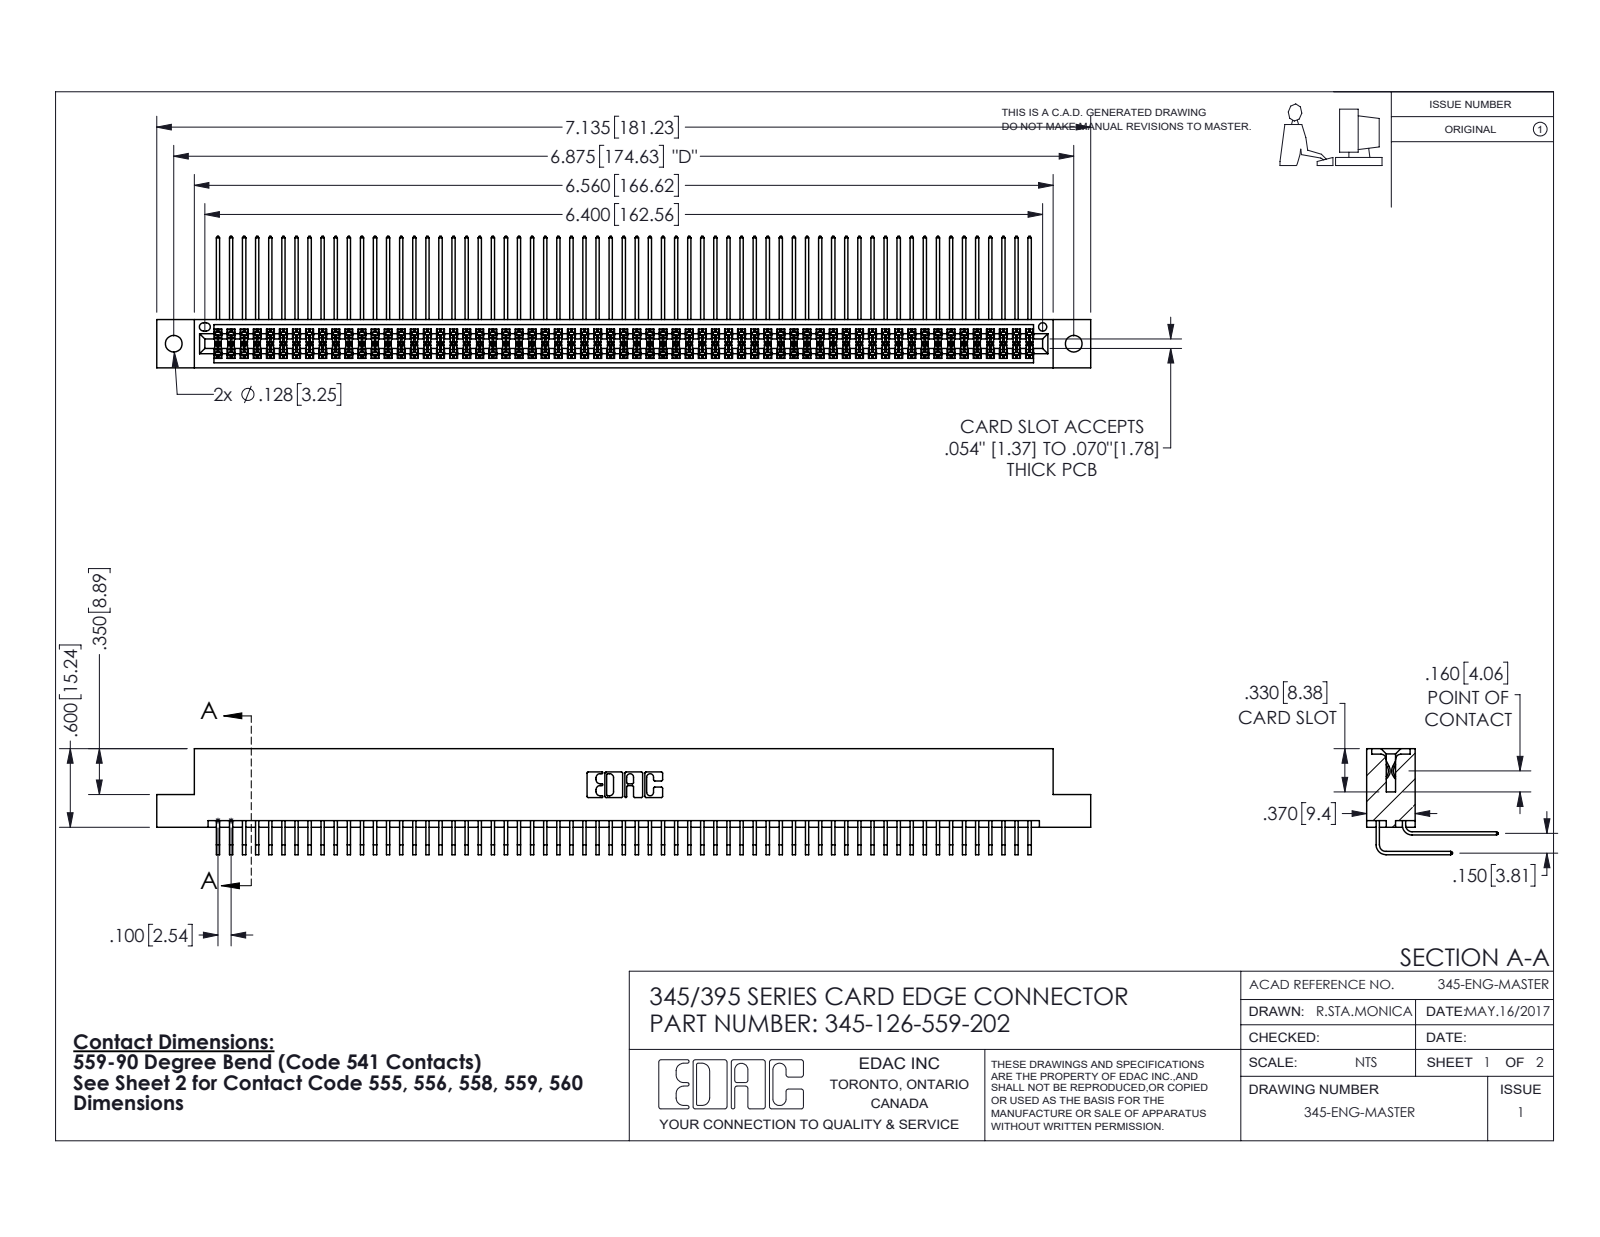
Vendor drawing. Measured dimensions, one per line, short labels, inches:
name: 345-126-559-202; 345-292-001_559 Tail - 2; 345 Part_Flush Mounting Lugs - 0.128 Dia; 345-292-001_558 559 Tail - 1
written by: SolidWorks 2016 (CONFIG_CONTROL_DESIGN)
unit: in
bodies: 127 solids, 6678 faces (4490 planar, 2188 cylindrical, 0 other)
size: 7.135 × 1.005 × 0.809
volume: 1.128 in³; area: 47.87 in²
holes: 2× ⌀0.128, 1× ⌀0.064
rounds: 251× R0.006, 22× R0.01, 6× R0.007, 6× R0.031, 3× R0.026, 2× R0.014, 2× R0.019, 2× R0.022
face distances: 0.072, 0.298, 0.2, 0.37, 0.098, 0.272, 0.025, 0.225, 0.175, 0.15
hole spacings: 0.27, 6.639, 6.875
